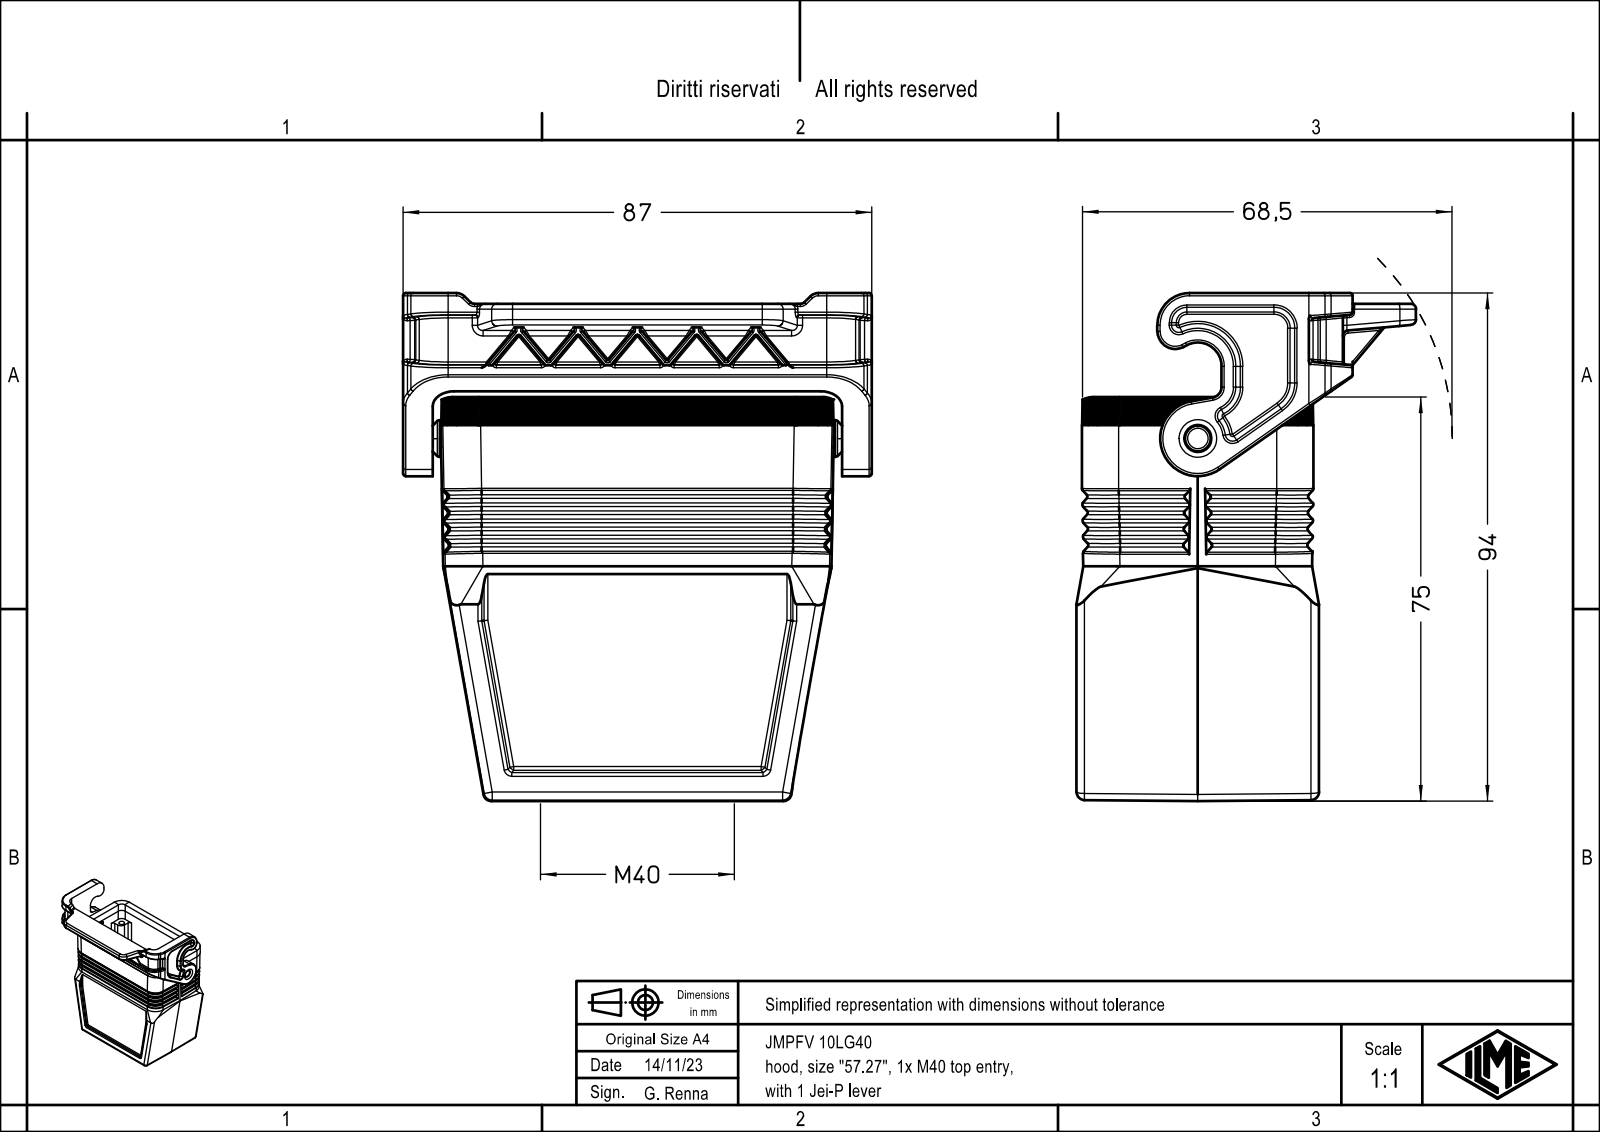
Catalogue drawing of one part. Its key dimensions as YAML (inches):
part_name: "JMPFV 10LG40"
step_written_by: "Creo Elements/Direct Modeling 20.1B 02-Apr-2019 (C) Parametric Technology GmbH (AUTOMOTIVE_DESIGN)"
units: inches
bodies: {solids: 1, faces: 1003, planar: 272, cylindrical: 357, other: 374}
overall_size: [3.711, 3.425, 2.48]
volume: 5.121
surface_area: 67.06
round_holes:
  - {diameter: 0.118, count: 4}
  - {diameter: 0.138, count: 4}
  - {diameter: 0.189, count: 1}
  - {diameter: 1.52, count: 1}
round_bosses_or_shafts:
  - {diameter: 0.268, count: 1}
partial_cylinders:
  - {radius: 0.02, count: 96}
  - {radius: 0.012, count: 71}
  - {radius: 0.039, count: 35}
  - {radius: 0.059, count: 24}
  - {radius: 0.013, count: 15}
  - {radius: 0.276, count: 13}
  - {radius: 0.118, count: 12}
  - {radius: 0.157, count: 8}
face_to_face_distances: [1.545, 0.148, 1.693, 0.039, 0.187, 0.276, 1.398, 0.079, 1.358, 1.506]
hole_center_spacings: [1.242, 1.063, 2.244, 2.483]
